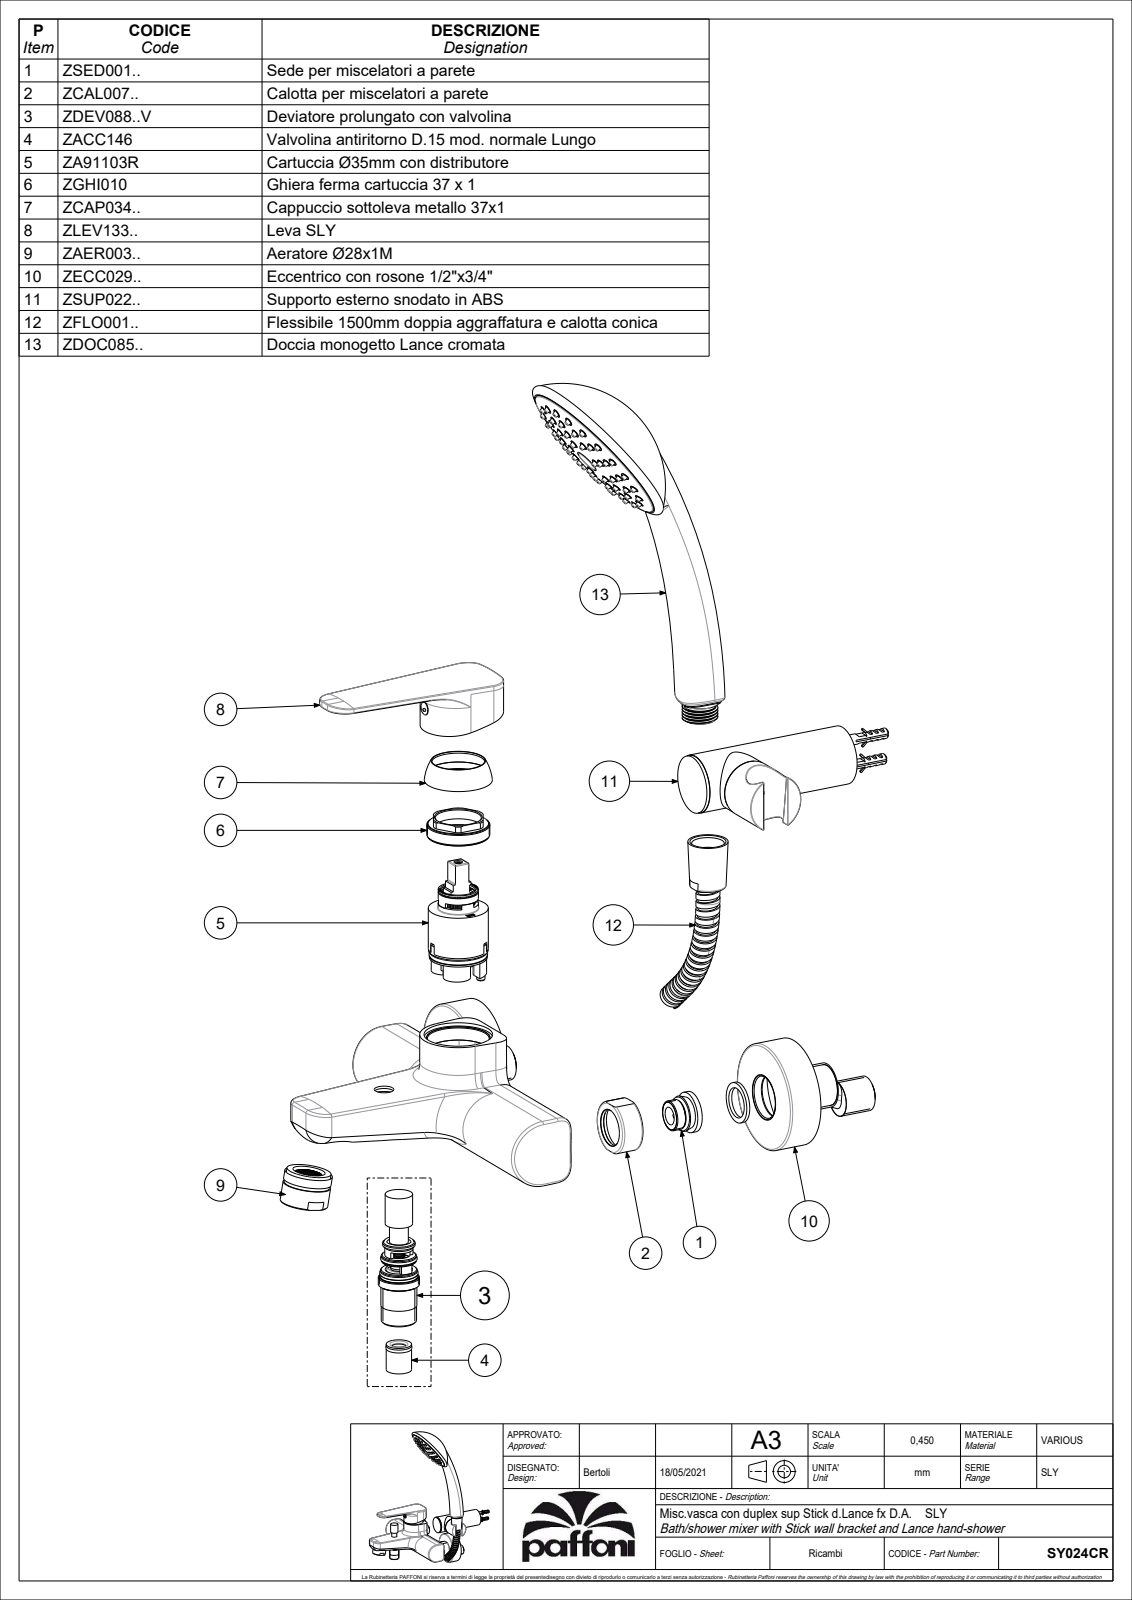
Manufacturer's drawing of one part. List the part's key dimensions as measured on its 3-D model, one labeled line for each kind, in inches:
Part name (STEP PRODUCT): SY024CR
STEP written by: CREO PARAMETRIC BY PTC INC, 2020044 (CONFIG_CONTROL_DESIGN)
Units: inches
Bodies: 6 solids, 4680 faces (2468 planar, 765 cylindrical, 1447 other)
Overall size (bounding box): 14.827 × 14.601 × 6.942
Volume: 31.38 in³ · Surface area: 465.6 in²
Round holes (diameter × count): ⌀0.197 ×52, ⌀0.472 ×4, ⌀0.354 ×3, ⌀0.965 ×3, ⌀0.984 ×3, ⌀0.13 ×2, ⌀0.157 ×2, ⌀0.315 ×2, ⌀0.413 ×2, ⌀0.63 ×2, ⌀0.65 ×2, ⌀0.709 ×2
Round bosses / shafts (diameter × count): ⌀0.197 ×16, ⌀0.945 ×3, ⌀2.5 ×2, ⌀1.331 ×2, ⌀1.063 ×2, ⌀0.394 ×2, ⌀3.74 ×1, ⌀3.646 ×1
Partial cylindrical surfaces — rounded edges, fillets, slot ends (radius × count): R0.02 ×44, R0.012 ×15, R0.006 ×11, R0.059 ×6, R0.039 ×4, R0.079 ×4, R0.197 ×4, R0.205 ×4
Main face-to-face distances: 0.138, 0.024, 0.591, 0.728, 0.614, 1.043, 0.118, 1.437, 0.752, 1.024
Hole centre spacings: 1.535, 1.22, 0.722, 0.315, 0.906, 0.63, 1.522, 0.48
